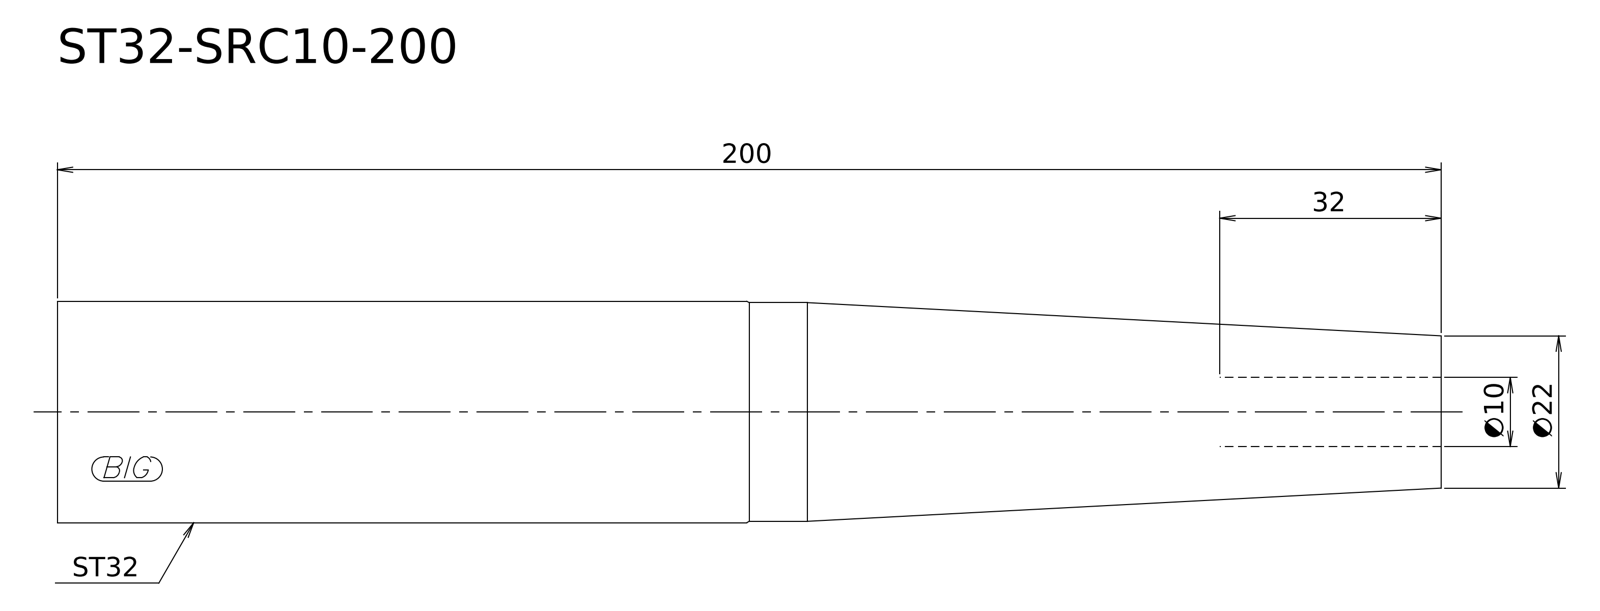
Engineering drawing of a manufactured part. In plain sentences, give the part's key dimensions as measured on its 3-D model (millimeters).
Its 3-D file was written by "Kubotek KeyCreator V8.5.1 (14335) (CONFIG_CONTROL_DESIGN)". It is 1 solid with 6 faces: 2 planar, 2 cylindrical and 2 other. Overall it measures 200 by 32 by 32 millimeters. Its volume is 139 236 cubic millimeters and its surface area 19 799 square millimeters. Round bosses or shafts: 1 of diameter 32, 1 of diameter 31.6. The main face-to-face distances are 200.
